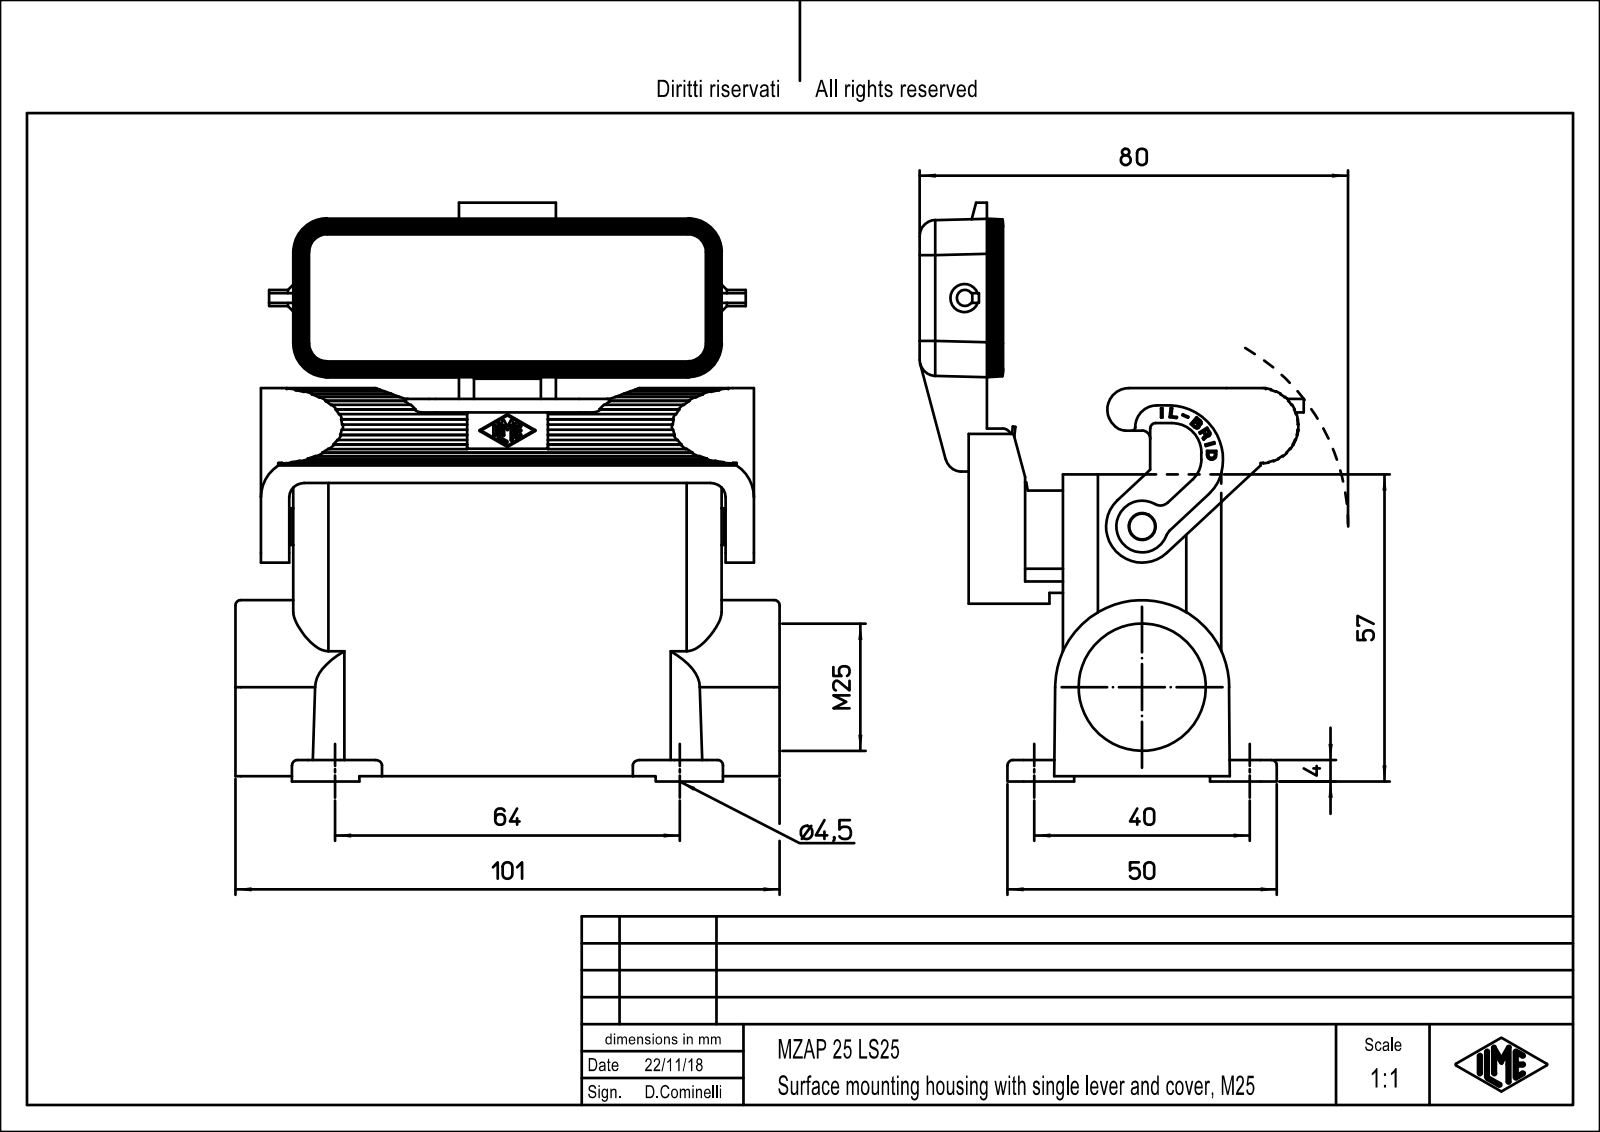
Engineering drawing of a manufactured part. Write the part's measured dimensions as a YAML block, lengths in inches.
part_name: "MZAP_25_LS25"
step_written_by: "PTC Creo Elements/Direct Modeling 19.0E 27-Jun-2016 (C) Parametric Technology GmbH (AUTOMOTIVE_DESIGN)"
units: inches
bodies: {solids: 1, faces: 849, planar: 591, cylindrical: 215, other: 43}
overall_size: [4.228, 3.976, 2.807]
volume: 5.542
surface_area: 87.17
round_holes:
  - {diameter: 0.118, count: 4}
  - {diameter: 0.177, count: 4}
  - {diameter: 0.197, count: 1}
  - {diameter: 0.827, count: 1}
  - {diameter: 0.929, count: 1}
round_bosses_or_shafts:
  - {diameter: 0.276, count: 1}
  - {diameter: 0.268, count: 1}
  - {diameter: 0.189, count: 1}
  - {diameter: 0.118, count: 1}
partial_cylinders:
  - {radius: 0.039, count: 17}
  - {radius: 0.008, count: 15}
  - {radius: 0.118, count: 12}
  - {radius: 0.138, count: 12}
  - {radius: 0.256, count: 8}
  - {radius: 0.02, count: 7}
  - {radius: 0.126, count: 4}
  - {radius: 0.236, count: 4}
face_to_face_distances: [0.109, 1.049, 1.157, 0.94, 2.205, 0.079, 0.118, 2.126, 2.017, 1.077]
hole_center_spacings: [0.474, 1.103, 2.602, 2.786, 0.63, 1.575, 2.52, 2.598]
